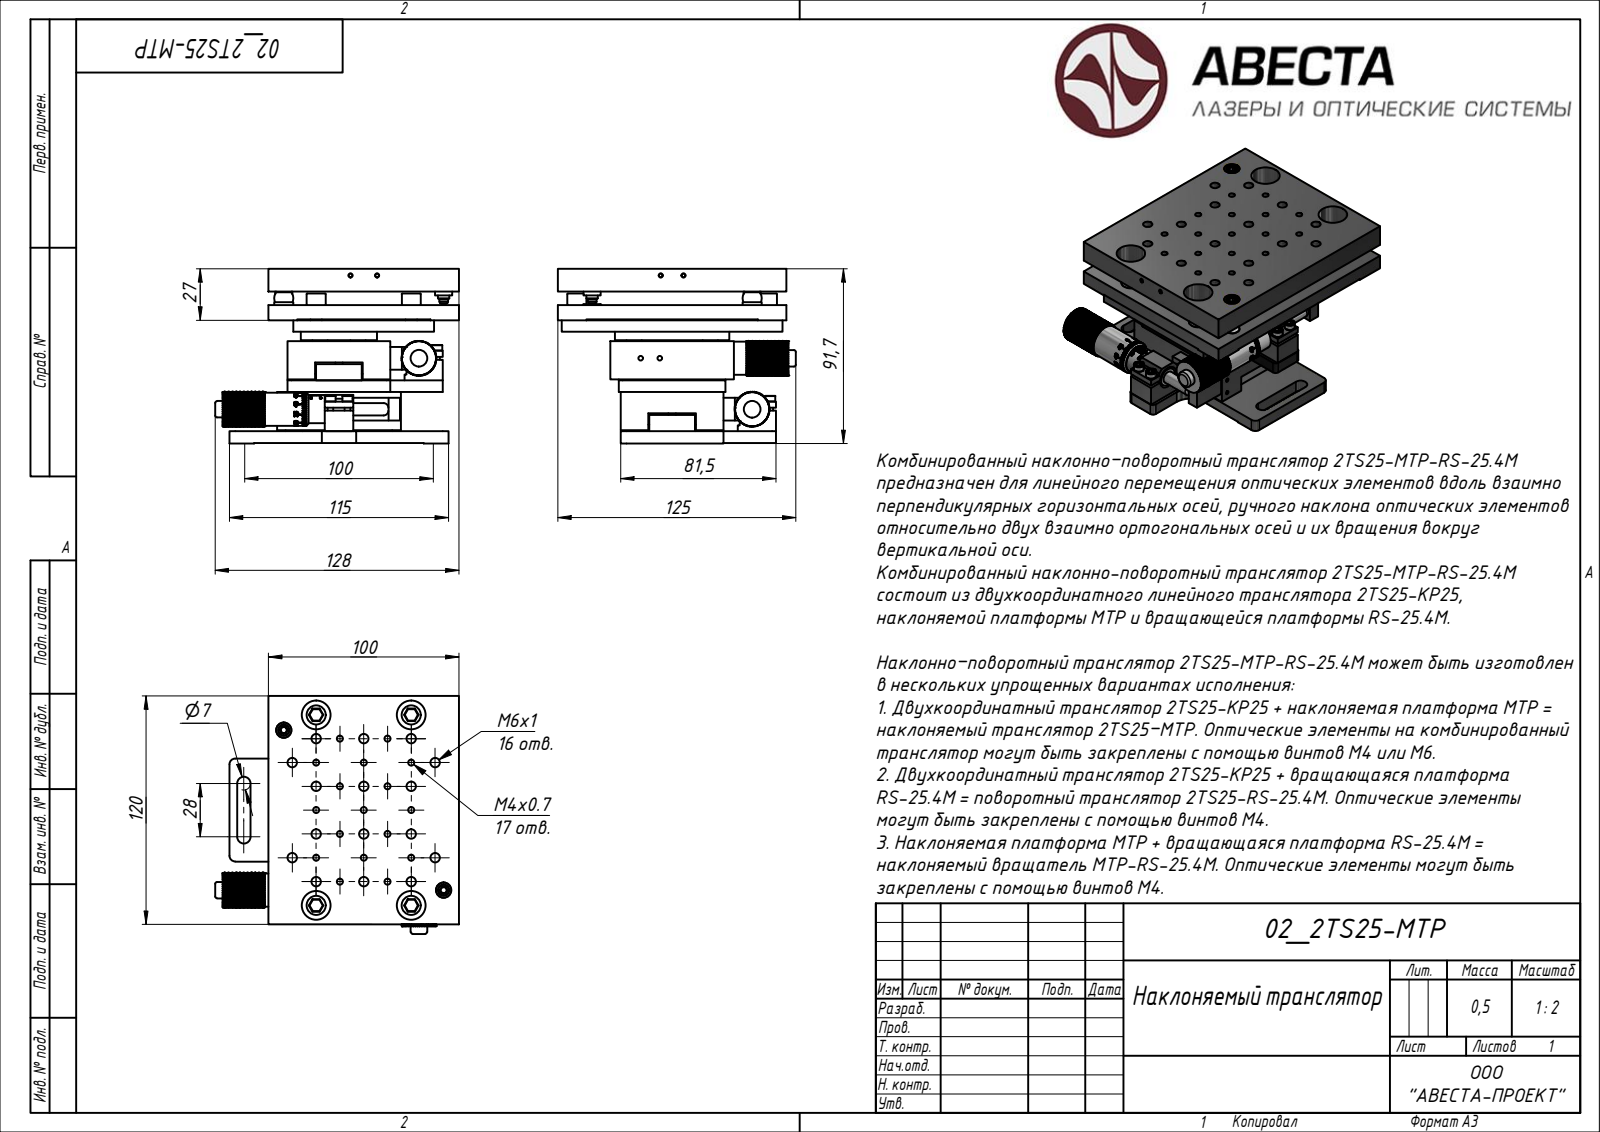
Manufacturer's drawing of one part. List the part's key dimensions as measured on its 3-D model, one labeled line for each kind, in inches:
STEP written by: Rhino 7.34 (AUTOMOTIVE_DESIGN)
Units: inches
Bodies: 1292 solids, 12345 faces (10586 planar, 1006 cylindrical, 753 other)
Overall size (bounding box): 5.039 × 4.921 × 3.61
Volume: 31.33 in³ · Surface area: 256.4 in²
Round holes (diameter × count): ⌀0.118 ×21, ⌀0.128 ×21, ⌀0.097 ×20, ⌀0.236 ×18, ⌀0.194 ×12, ⌀0.097 ×10, ⌀0.256 ×8, ⌀0.591 ×6, ⌀0.276 ×5, ⌀0.079 ×4, ⌀0.087 ×4, ⌀0.138 ×4
Round bosses / shafts (diameter × count): ⌀0.213 ×22, ⌀0.097 ×18, ⌀0.236 ×8, ⌀0.138 ×8, ⌀0.126 ×8, ⌀0.394 ×7, ⌀0.079 ×7, ⌀0.098 ×6
Partial cylindrical surfaces — rounded edges, fillets, slot ends (radius × count): R0.079 ×8, R0.043 ×6, R0.049 ×4, R0.118 ×4, R0.138 ×4, R0.394 ×4, R0.04 ×3, R0.04 ×3
Main face-to-face distances: 0.02, 0.276, 0.748, 0.472, 0.295, 1.043, 0.315, 0.571, 0.591, 1.063
Hole centre spacings: 0.88, 0.557, 0.787, 0.394, 1.484, 0.335, 0.378, 0.426
